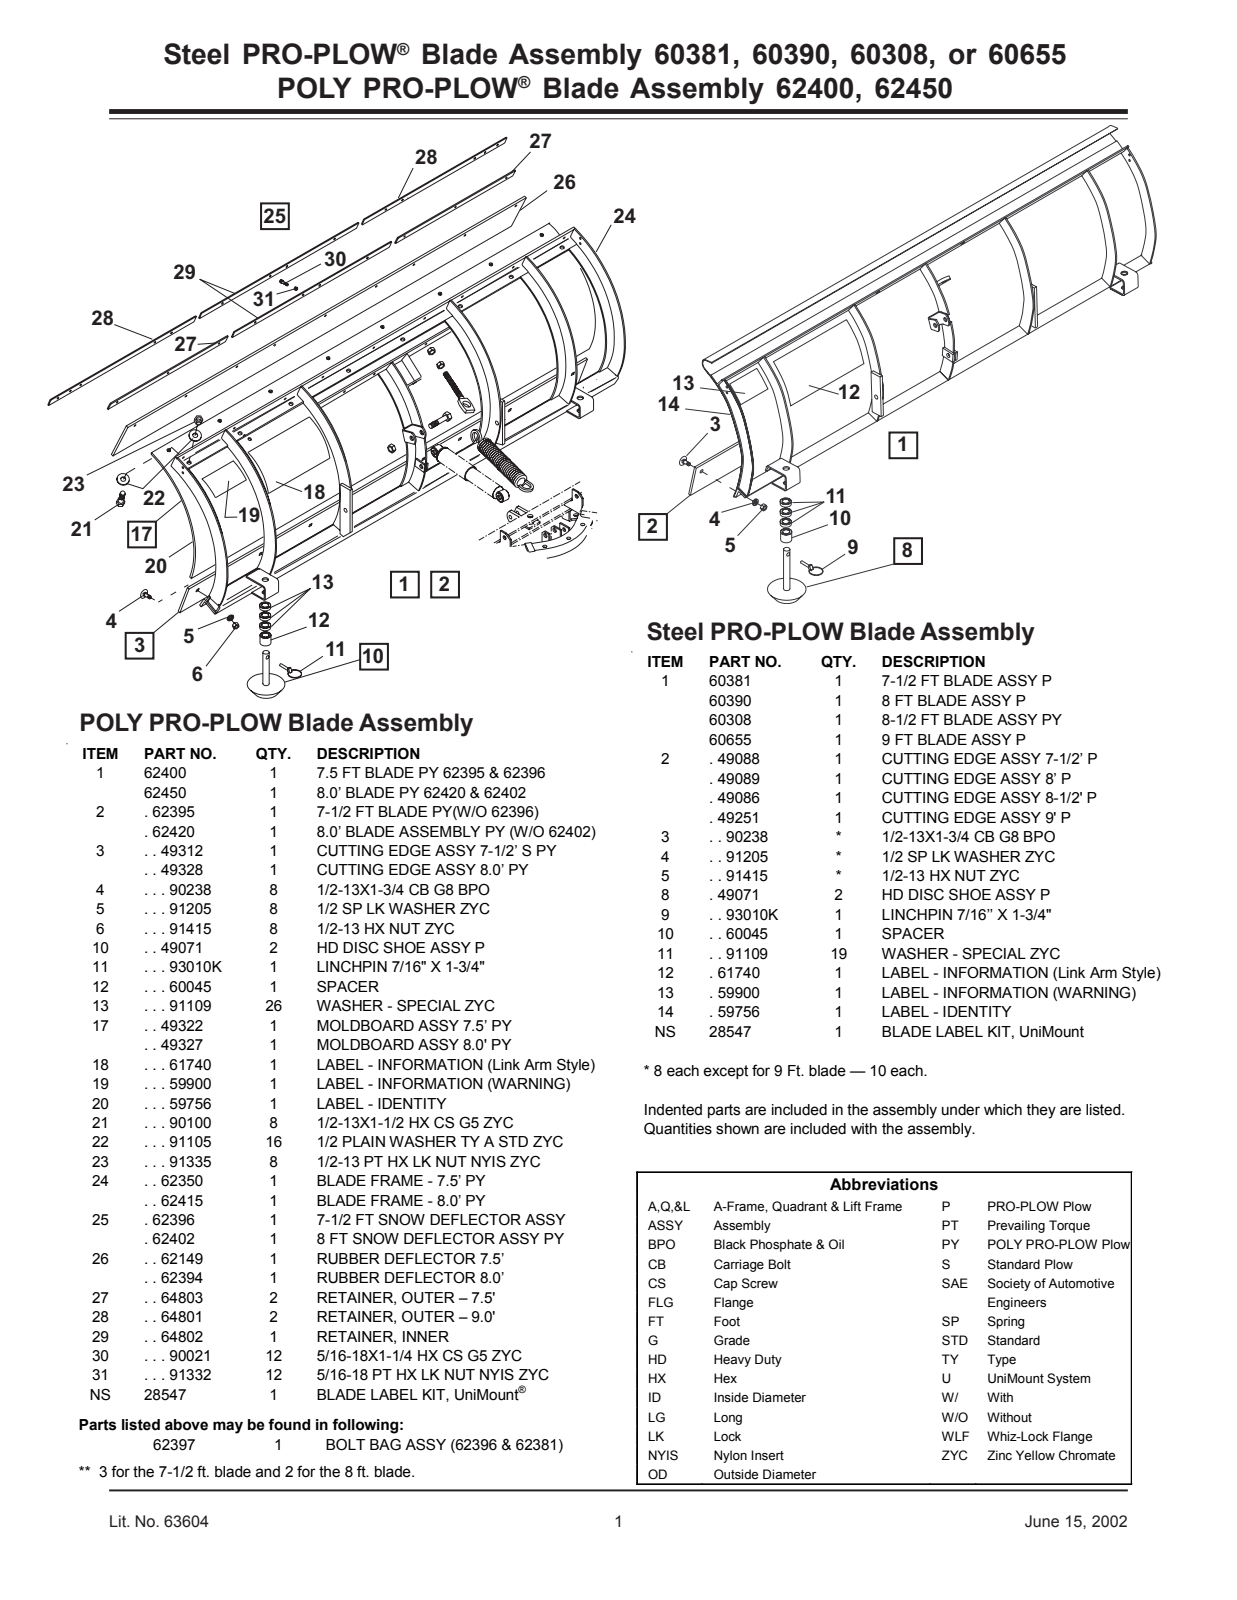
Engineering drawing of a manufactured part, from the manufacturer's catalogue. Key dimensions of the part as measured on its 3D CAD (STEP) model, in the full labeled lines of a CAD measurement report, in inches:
STEP written by: ACIS (automotive_design)
Units: inches
Bodies: 2 solids, 26 faces (8 planar, 10 cylindrical, 8 other)
Overall size (bounding box): 2.126 × 0.157 × 0.157
Volume: 0.04 in³ · Surface area: 1.1 in²
Round bosses / shafts (diameter × count): ⌀0.157 ×1
Partial cylindrical surfaces — rounded edges, fillets, slot ends (radius × count): R0.013 ×1, R0.021 ×1, R0.028 ×1, R0.075 ×1
Main face-to-face distances: 1.594, 0.211, 1.383
